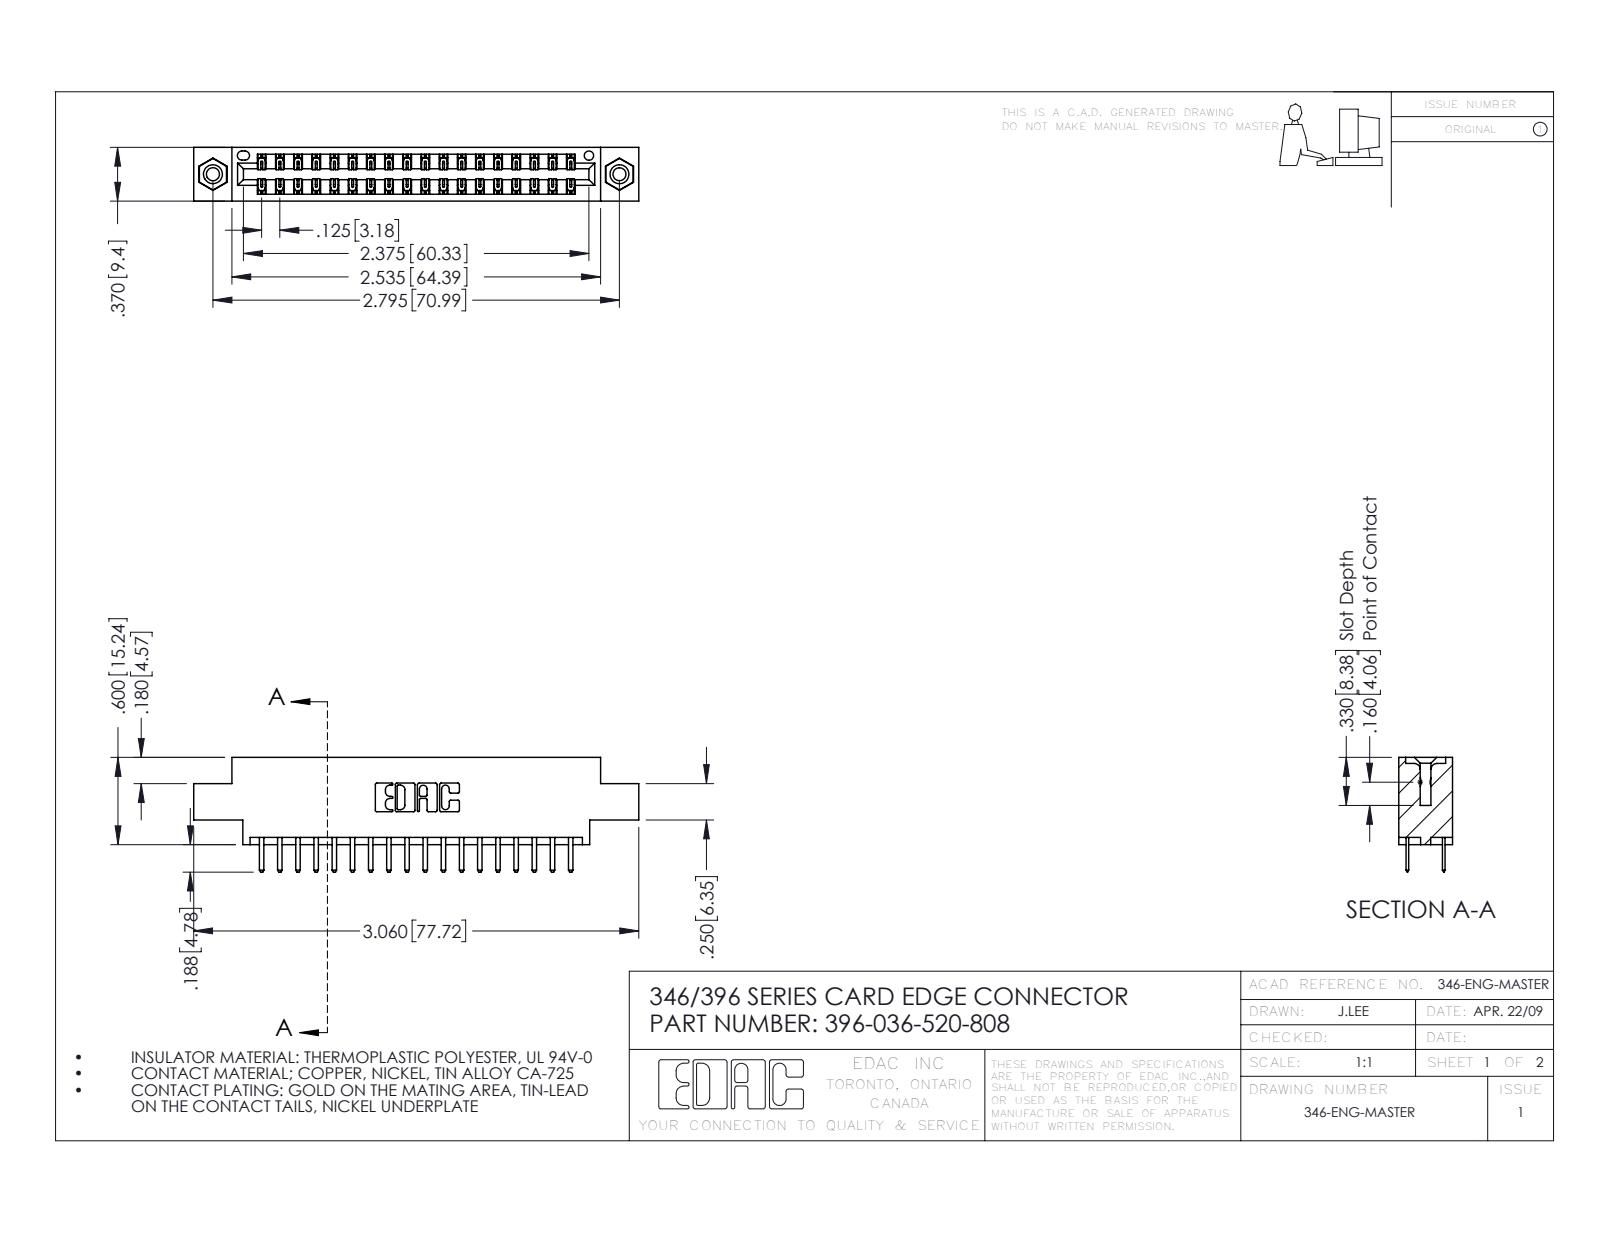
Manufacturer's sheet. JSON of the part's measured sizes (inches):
{"part_name": "345-250-001_345-250-003-102; 345-292-001_345-293-120; 396-036-520-808; 346 Part_0.170 Offset - 0.156 Dia-TI", "step_written_by": "SolidWorks 2016 (CONFIG_CONTROL_DESIGN)", "units": "inches", "bodies": {"solids": 39, "faces": 2202, "planar": 1444, "cylindrical": 742, "other": 16}, "overall_size": [3.06, 0.788, 0.37], "volume_in3": 0.44, "surface_area_in2": 15.04, "round_holes": [[0.089, 2], [0.125, 2], [0.156, 2], [0.064, 1]], "round_bosses_or_shafts": [[0.155, 2]], "partial_cylinders_radius": [[0.006, 54], [0.01, 40], [0.01, 22], [0.007, 6], [0.031, 6], [0.026, 3], [0.014, 2], [0.022, 2]], "face_to_face_distances": [0.048, 0.322, 0.25, 0.37, 0.222, 0.275, 0.072, 0.298, 0.025, 0.148], "hole_center_spacings": [0.246, 2.588, 2.795]}
